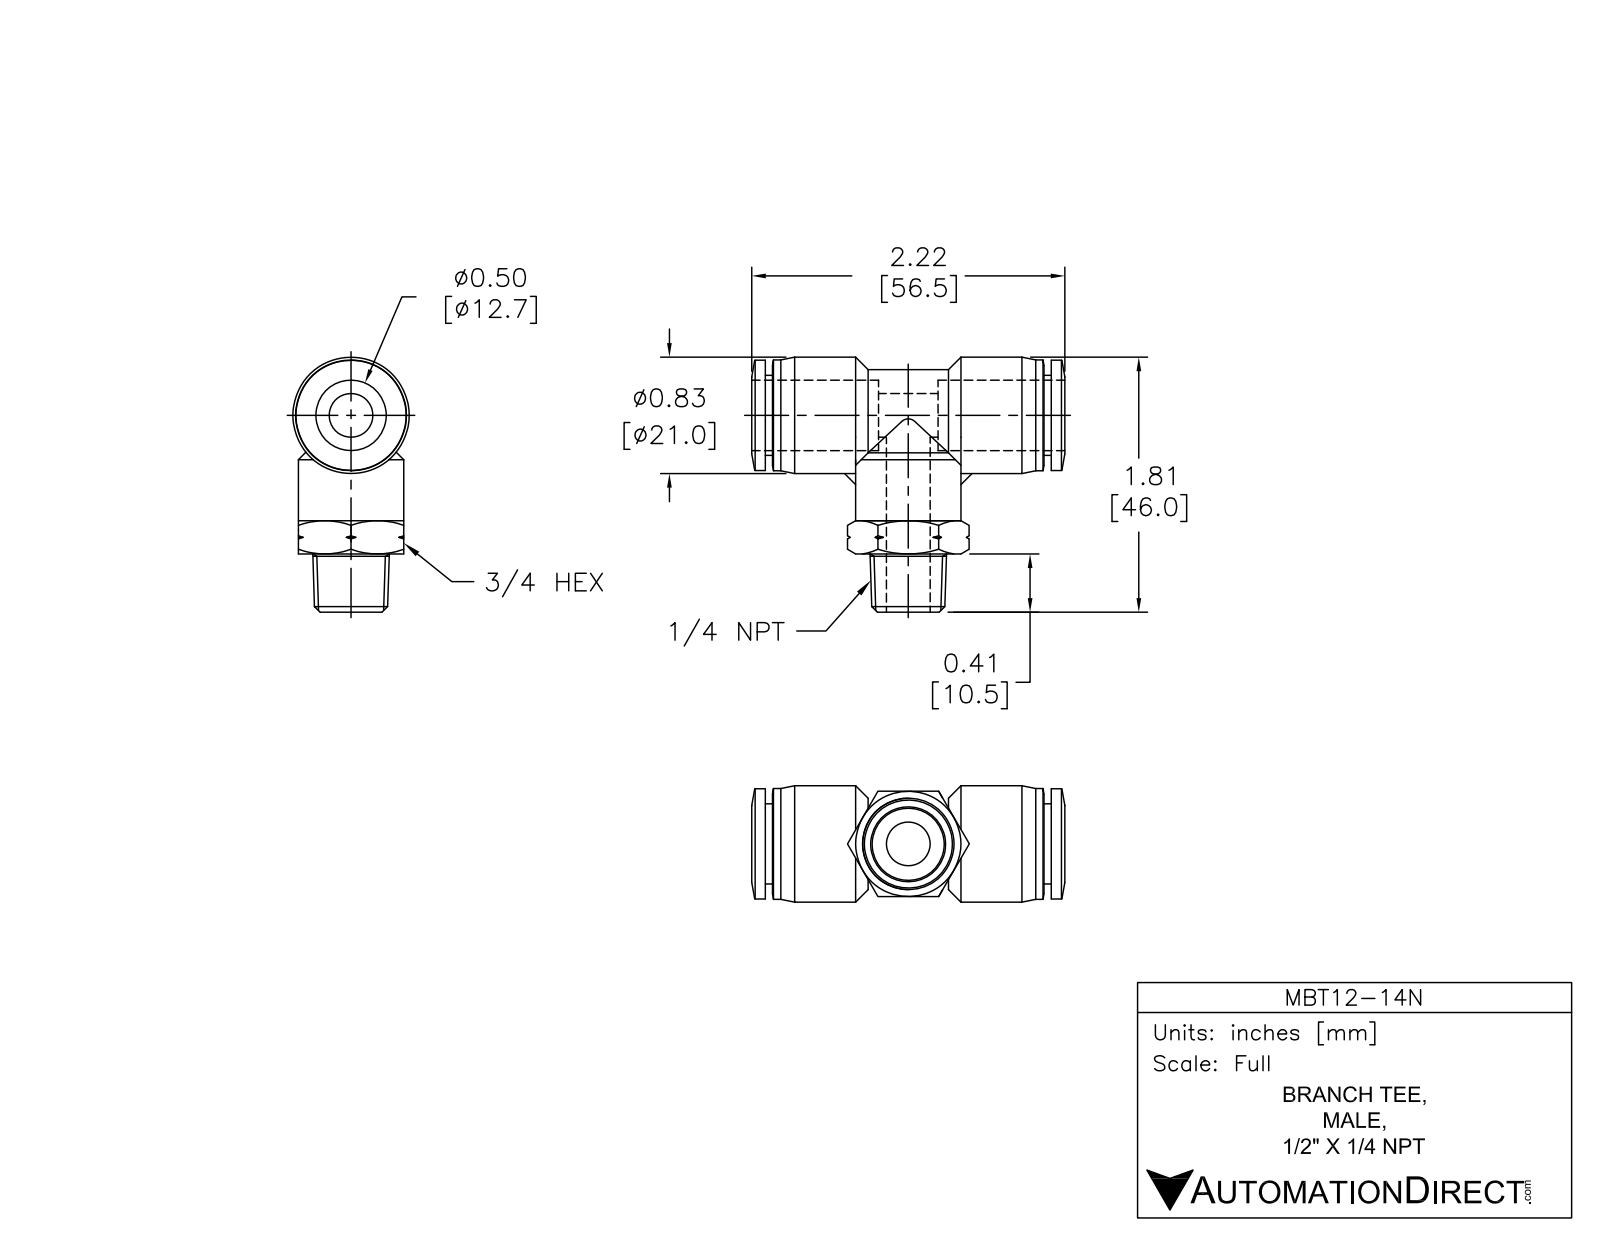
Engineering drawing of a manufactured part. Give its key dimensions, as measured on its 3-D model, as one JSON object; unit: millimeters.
{"part_name": "MBT12-14N", "step_written_by": "SolidWorks 2015 (AUTOMOTIVE_DESIGN)", "units": "millimeters", "bodies": {"solids": 1, "faces": 109, "planar": 20, "cylindrical": 31, "other": 58}, "overall_size": [56.5, 46, 21], "volume_mm3": 14900, "surface_area_mm2": 8974, "round_holes": [[8, 2], [13, 1]], "round_bosses_or_shafts": [[21, 1], [20, 1], [19.9, 1], [19, 1], [16.5, 1], [14.5, 1]], "partial_cylinders_radius": [[8.3, 1]], "face_to_face_distances": [1.3, 50.3, 19, 20.7, 31, 19.4, 29.6, 51.6, 49, 10.3]}
